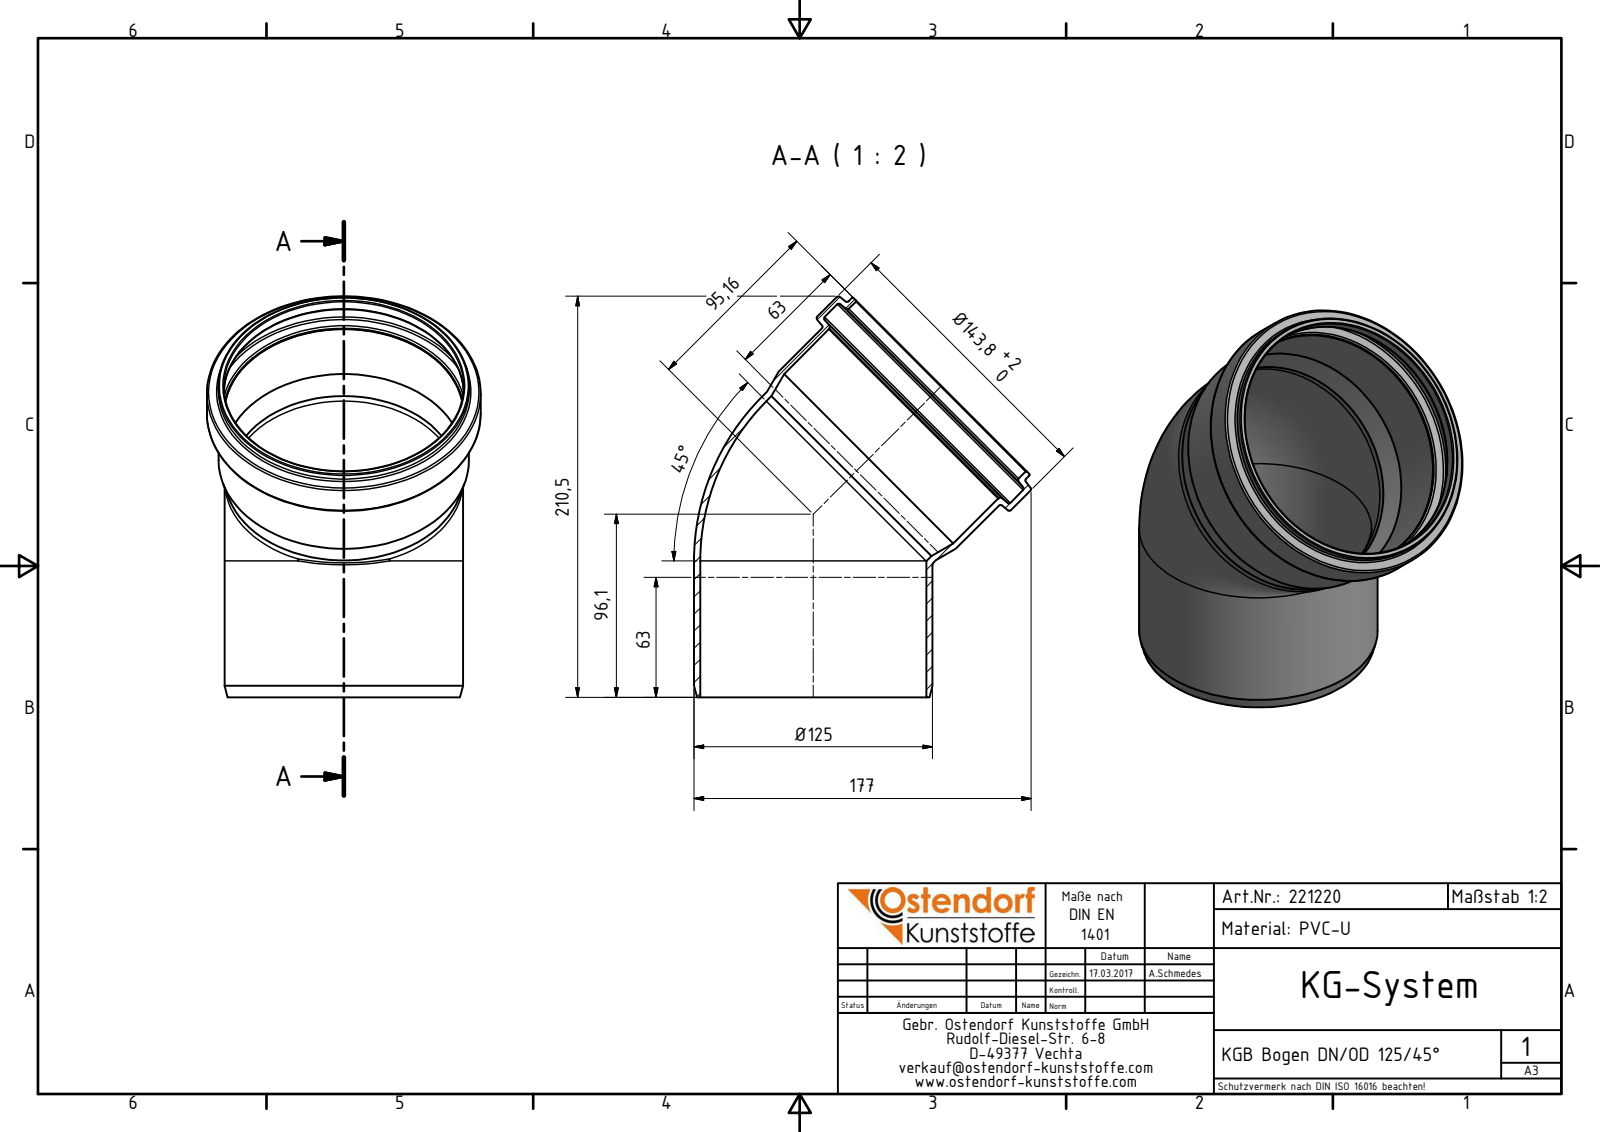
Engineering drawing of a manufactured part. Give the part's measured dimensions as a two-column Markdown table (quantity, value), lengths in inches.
| quantity | value |
| --- | --- |
| part name | 221220 KGB Bogen DN_OD 125_45° |
| STEP written by | Autodesk Inventor 2016 (AUTOMOTIVE_DESIGN) |
| units | inches |
| bodies | 1 solid, 34 faces (3 planar, 11 cylindrical, 20 other) |
| overall size | 8.287 × 6.969 × 5.661 |
| volume | 13.79 in³ |
| surface area | 245.7 in² |
| round holes (diameter × count) | 4.677 × 2, 4.949 × 1, 4.961 × 1, 5.433 × 1 |
| round bosses / shafts (diameter × count) | 4.929 × 2, 5.661 × 1, 5.189 × 1, 5.177 × 1 |
| main face-to-face distances | 0.814 |
